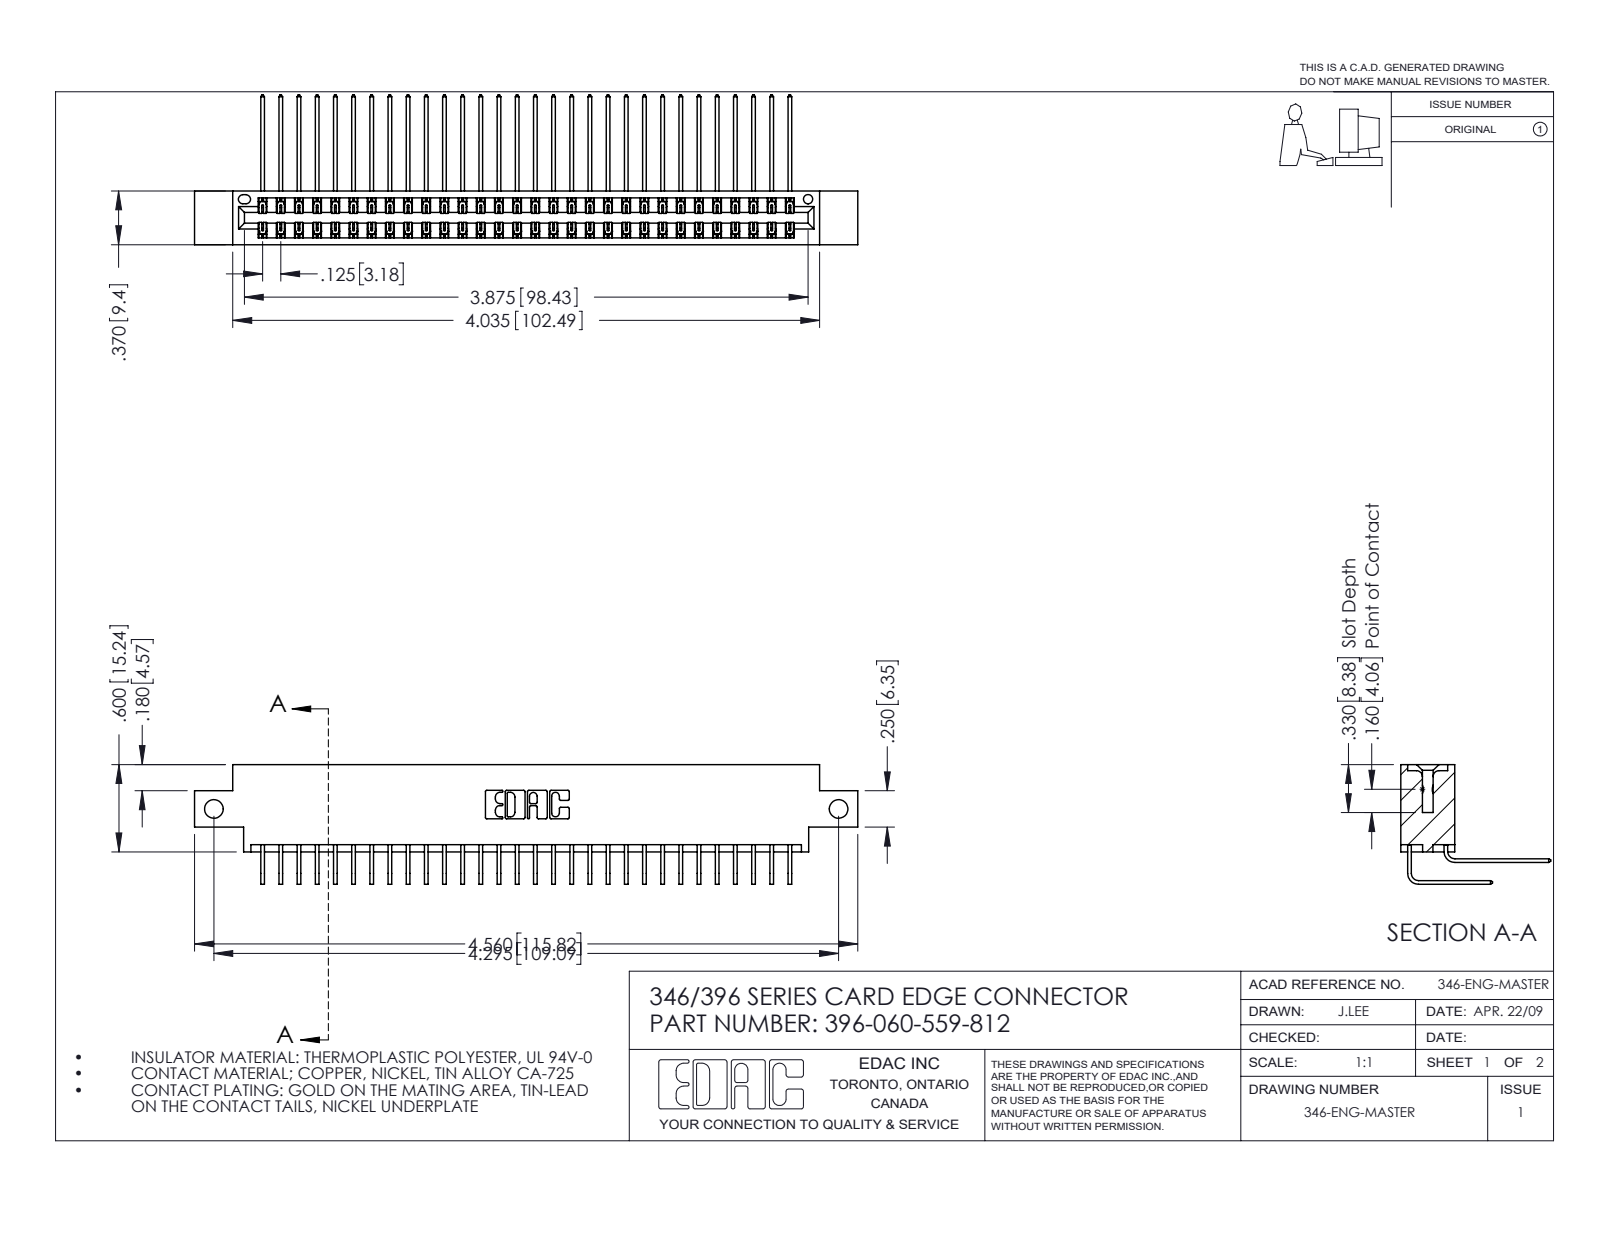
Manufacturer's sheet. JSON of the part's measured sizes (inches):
{"part_name": "345-292-001_558 559 Tail - 1; 396-060-559-812; 346 Part_0.170 Offset - Side Mount; 345-292-001_559 Tail - 2", "step_written_by": "SolidWorks 2016 (CONFIG_CONTROL_DESIGN)", "units": "inches", "bodies": {"solids": 61, "faces": 3366, "planar": 2300, "cylindrical": 1066, "other": 0}, "overall_size": [4.56, 1.03, 0.823], "volume_in3": 0.69, "surface_area_in2": 26.43, "round_holes": [[0.128, 2], [0.064, 1]], "partial_cylinders_radius": [[0.006, 90], [0.01, 22], [0.007, 6], [0.031, 6], [0.026, 3], [0.014, 2], [0.022, 2], [0.024, 2]], "face_to_face_distances": [0.048, 0.322, 0.025, 0.37, 0.25, 0.072, 0.298, 0.275, 0.148, 0.222], "hole_center_spacings": [4.295]}
